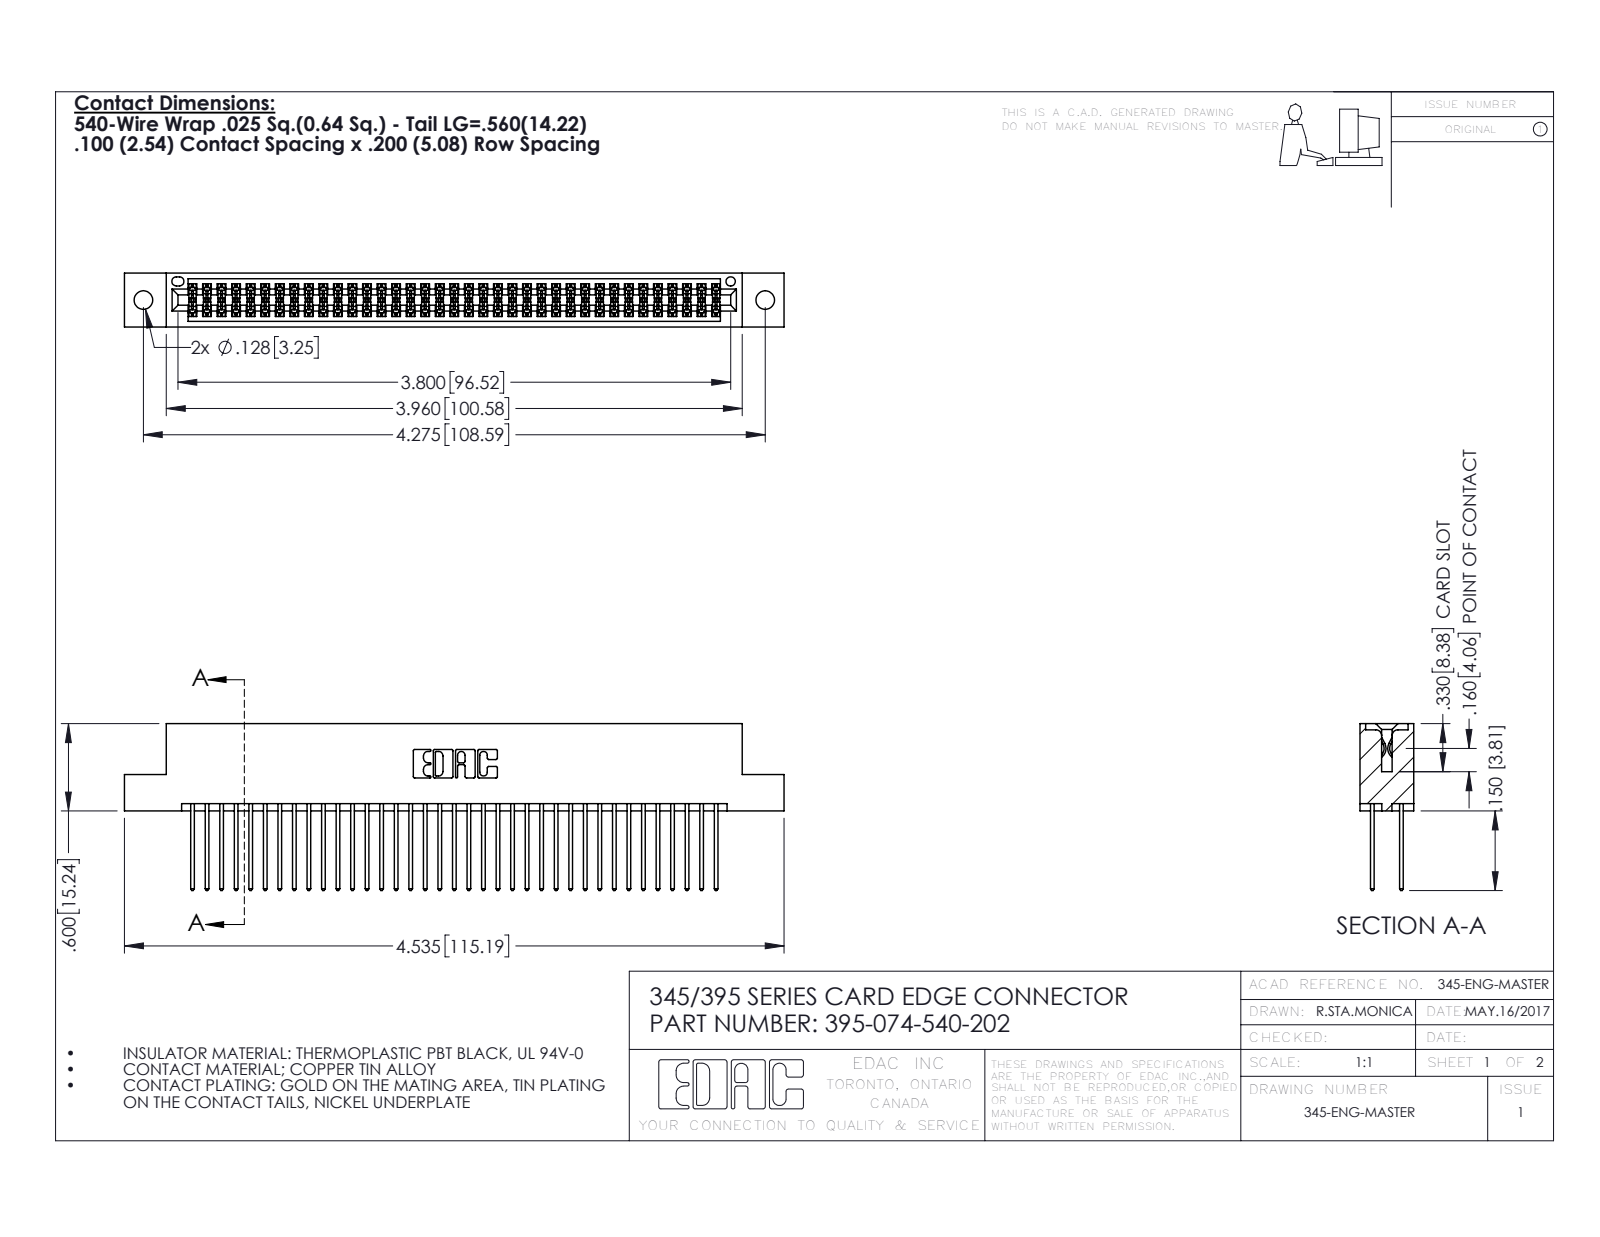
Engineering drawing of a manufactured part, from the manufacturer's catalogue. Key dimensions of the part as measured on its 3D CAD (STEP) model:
Part name (STEP PRODUCT): 345 Part_Flush Mounting Lugs - 0.128 Dia; 395-074-540-202; 345-292-001_345-293-140
STEP written by: SolidWorks 2016 (CONFIG_CONTROL_DESIGN)
Units: inches
Bodies: 75 solids, 3826 faces (2522 planar, 1304 cylindrical, 0 other)
Overall size (bounding box): 4.535 × 1.147 × 0.37
Volume: 0.695 in³ · Surface area: 27.53 in²
Round holes (diameter × count): ⌀0.128 ×2, ⌀0.064 ×1
Partial cylindrical surfaces — rounded edges, fillets, slot ends (radius × count): R0.006 ×111, R0.01 ×74, R0.01 ×22, R0.007 ×6, R0.031 ×6, R0.026 ×3, R0.014 ×2, R0.019 ×2
Main face-to-face distances: 0.298, 0.072, 0.2, 0.098, 0.272, 0.025, 0.37, 0.225, 0.175, 0.149
Hole centre spacings: 0.27, 4.039, 4.275
